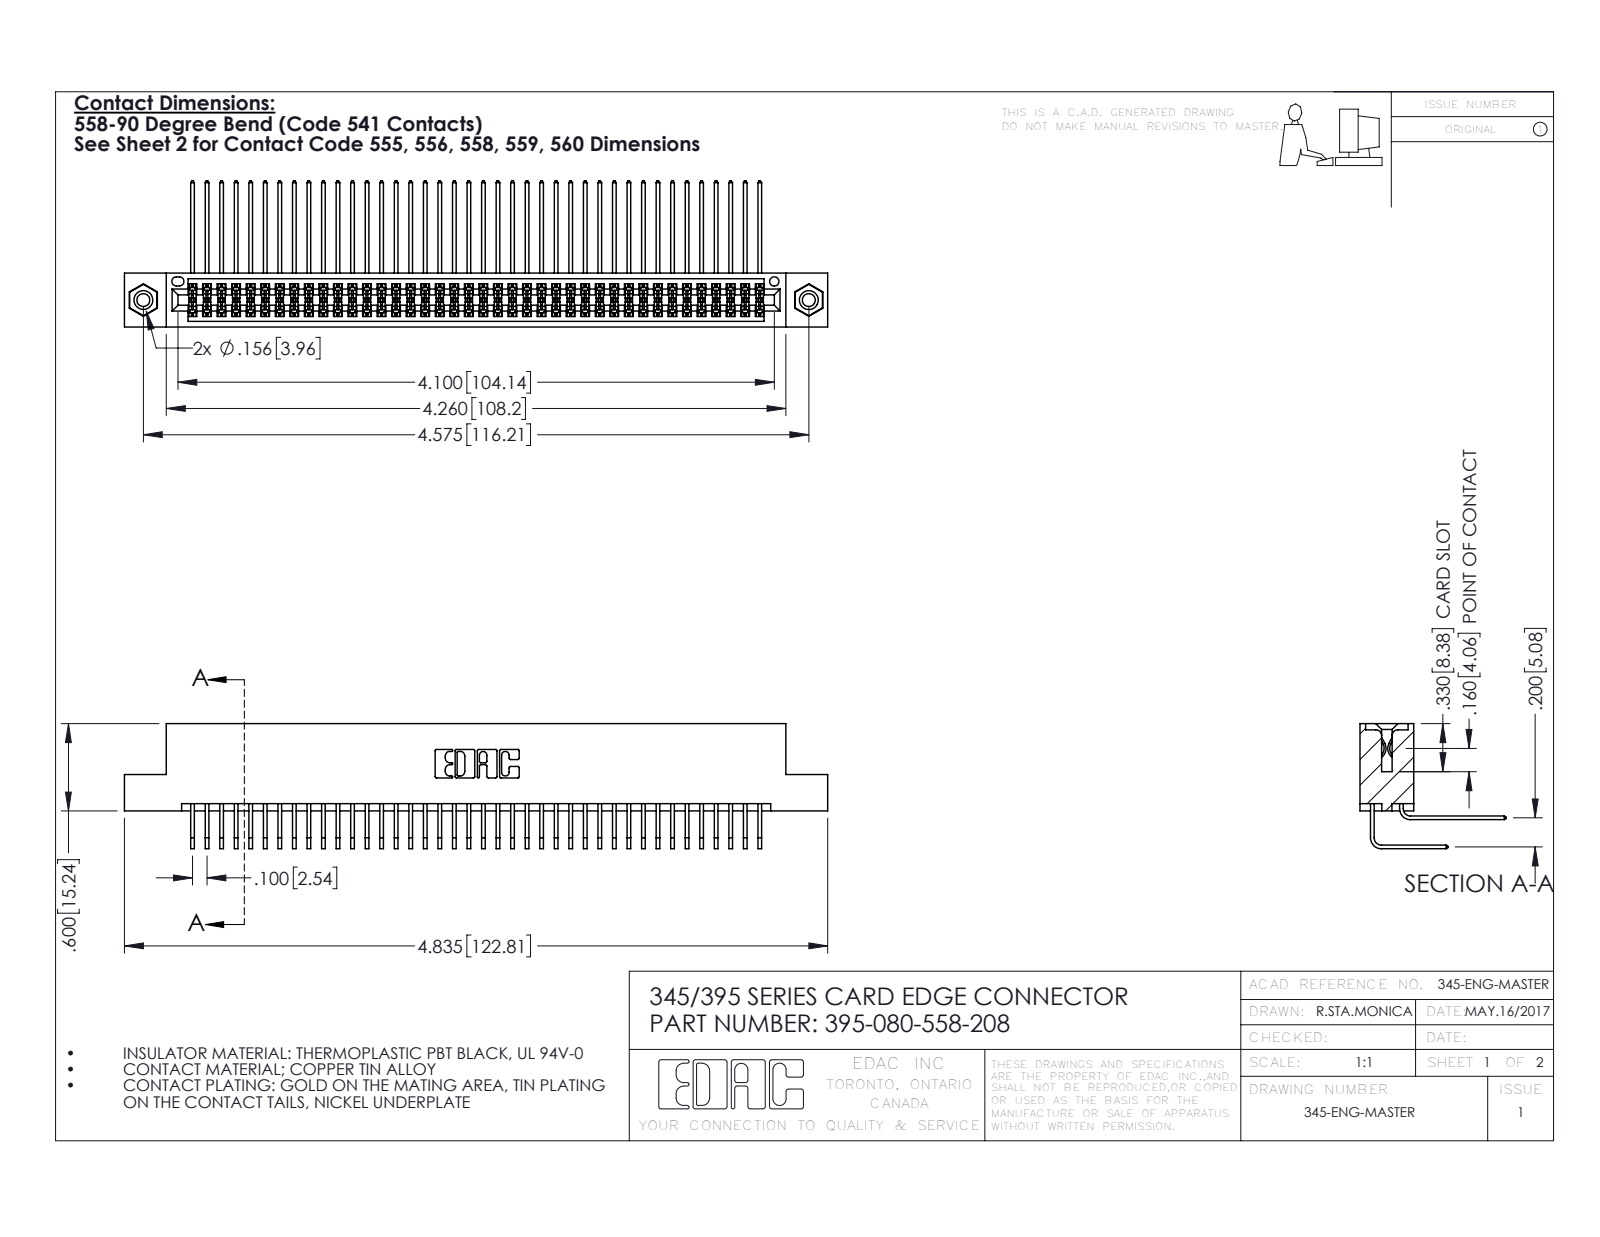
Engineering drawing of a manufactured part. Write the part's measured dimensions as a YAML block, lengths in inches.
part_name: "345-250-001_345-250-003-102; 345 Part_Flush Mounting Lugs - 0.156 Dia-TI; 395-080-558-208; 345-292-001_558 559 Tail - 1 (+1 more)"
step_written_by: "SolidWorks 2016 (CONFIG_CONTROL_DESIGN)"
units: inches
bodies: {solids: 83, faces: 4346, planar: 2912, cylindrical: 1418, other: 16}
overall_size: [4.835, 1.005, 0.859]
volume: 0.755
surface_area: 31.66
round_holes:
  - {diameter: 0.089, count: 2}
  - {diameter: 0.125, count: 2}
  - {diameter: 0.156, count: 2}
  - {diameter: 0.064, count: 1}
round_bosses_or_shafts:
  - {diameter: 0.155, count: 2}
partial_cylinders:
  - {radius: 0.006, count: 121}
  - {radius: 0.01, count: 22}
  - {radius: 0.007, count: 6}
  - {radius: 0.031, count: 6}
  - {radius: 0.026, count: 3}
  - {radius: 0.014, count: 2}
  - {radius: 0.019, count: 2}
  - {radius: 0.022, count: 2}
face_to_face_distances: [0.072, 0.298, 0.2, 0.37, 0.098, 0.272, 0.025, 0.225, 0.025, 0.175]
hole_center_spacings: [0.27, 4.339, 4.575]
